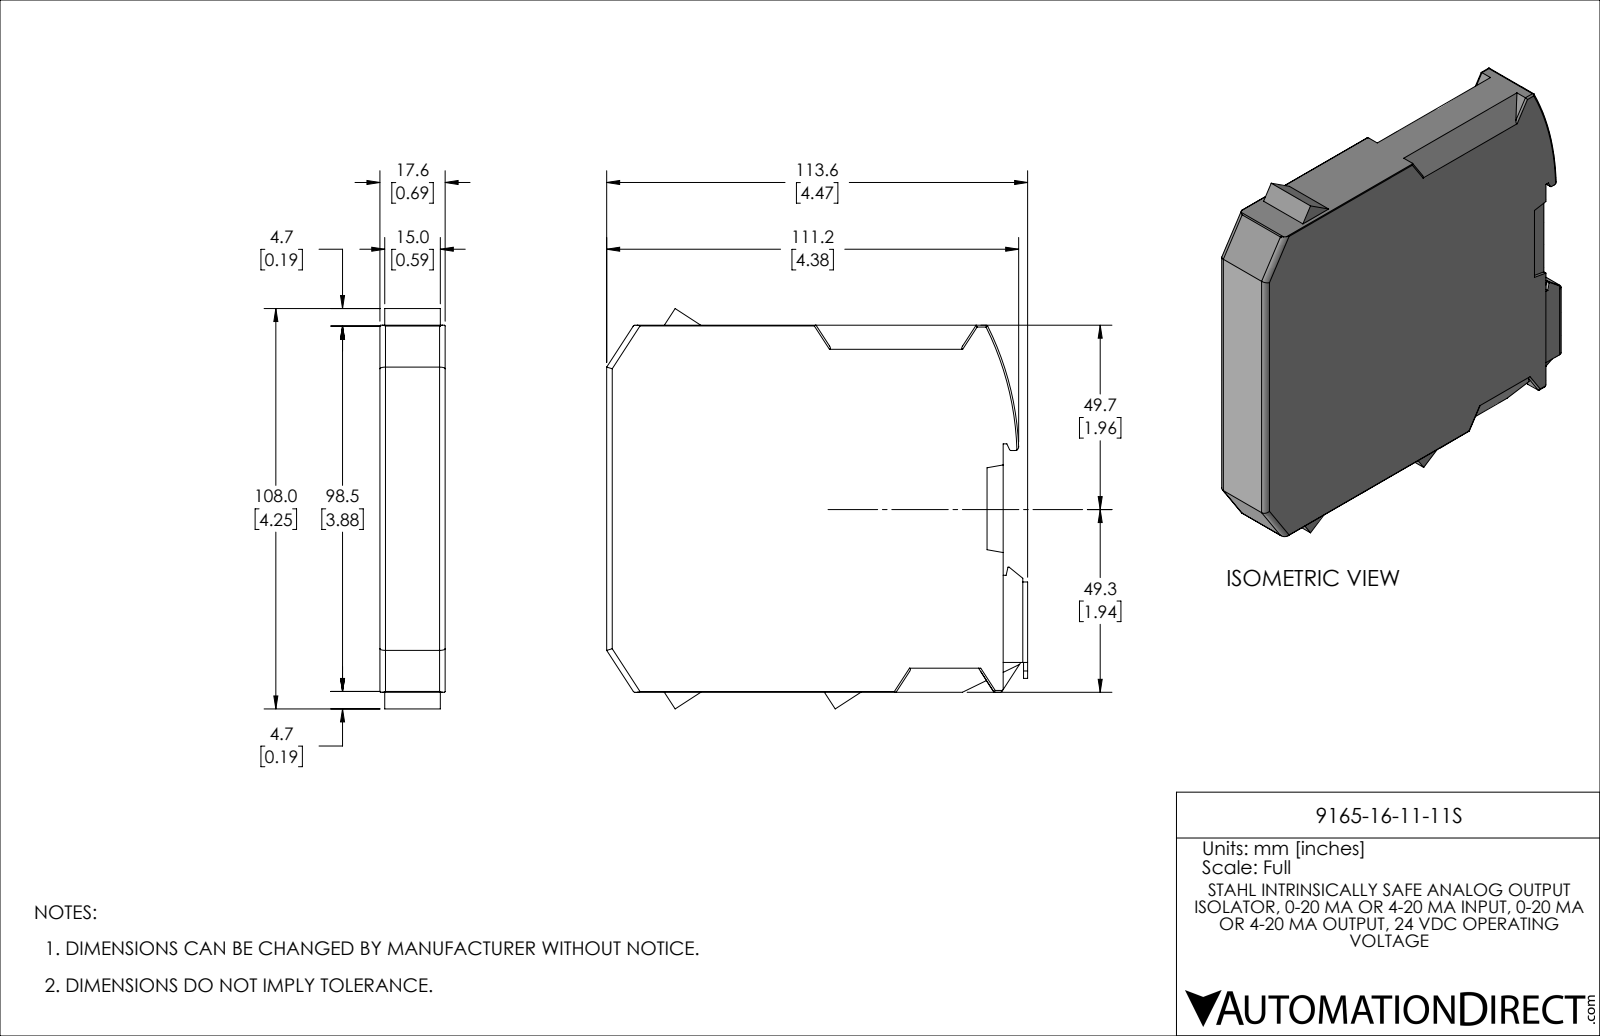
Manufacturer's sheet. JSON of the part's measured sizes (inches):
{"part_name": "9165-16-11-11S", "step_written_by": "SolidWorks 2021 (AUTOMOTIVE_DESIGN)", "units": "inches", "bodies": {"solids": 1, "faces": 171, "planar": 117, "cylindrical": 52, "other": 2}, "overall_size": [4.472, 4.251, 0.693], "volume_in3": 11.4, "surface_area_in2": 45.56, "partial_cylinders_radius": [[0.02, 17], [0.059, 6], [0.008, 4], [0.028, 4], [0.051, 2], [0.079, 2], [0.039, 1], [3.15, 1]], "face_to_face_distances": [0.693, 3.898, 4.213, 0.043, 0.26, 4.472, 0.217, 4.429, 0.059, 2.293]}
